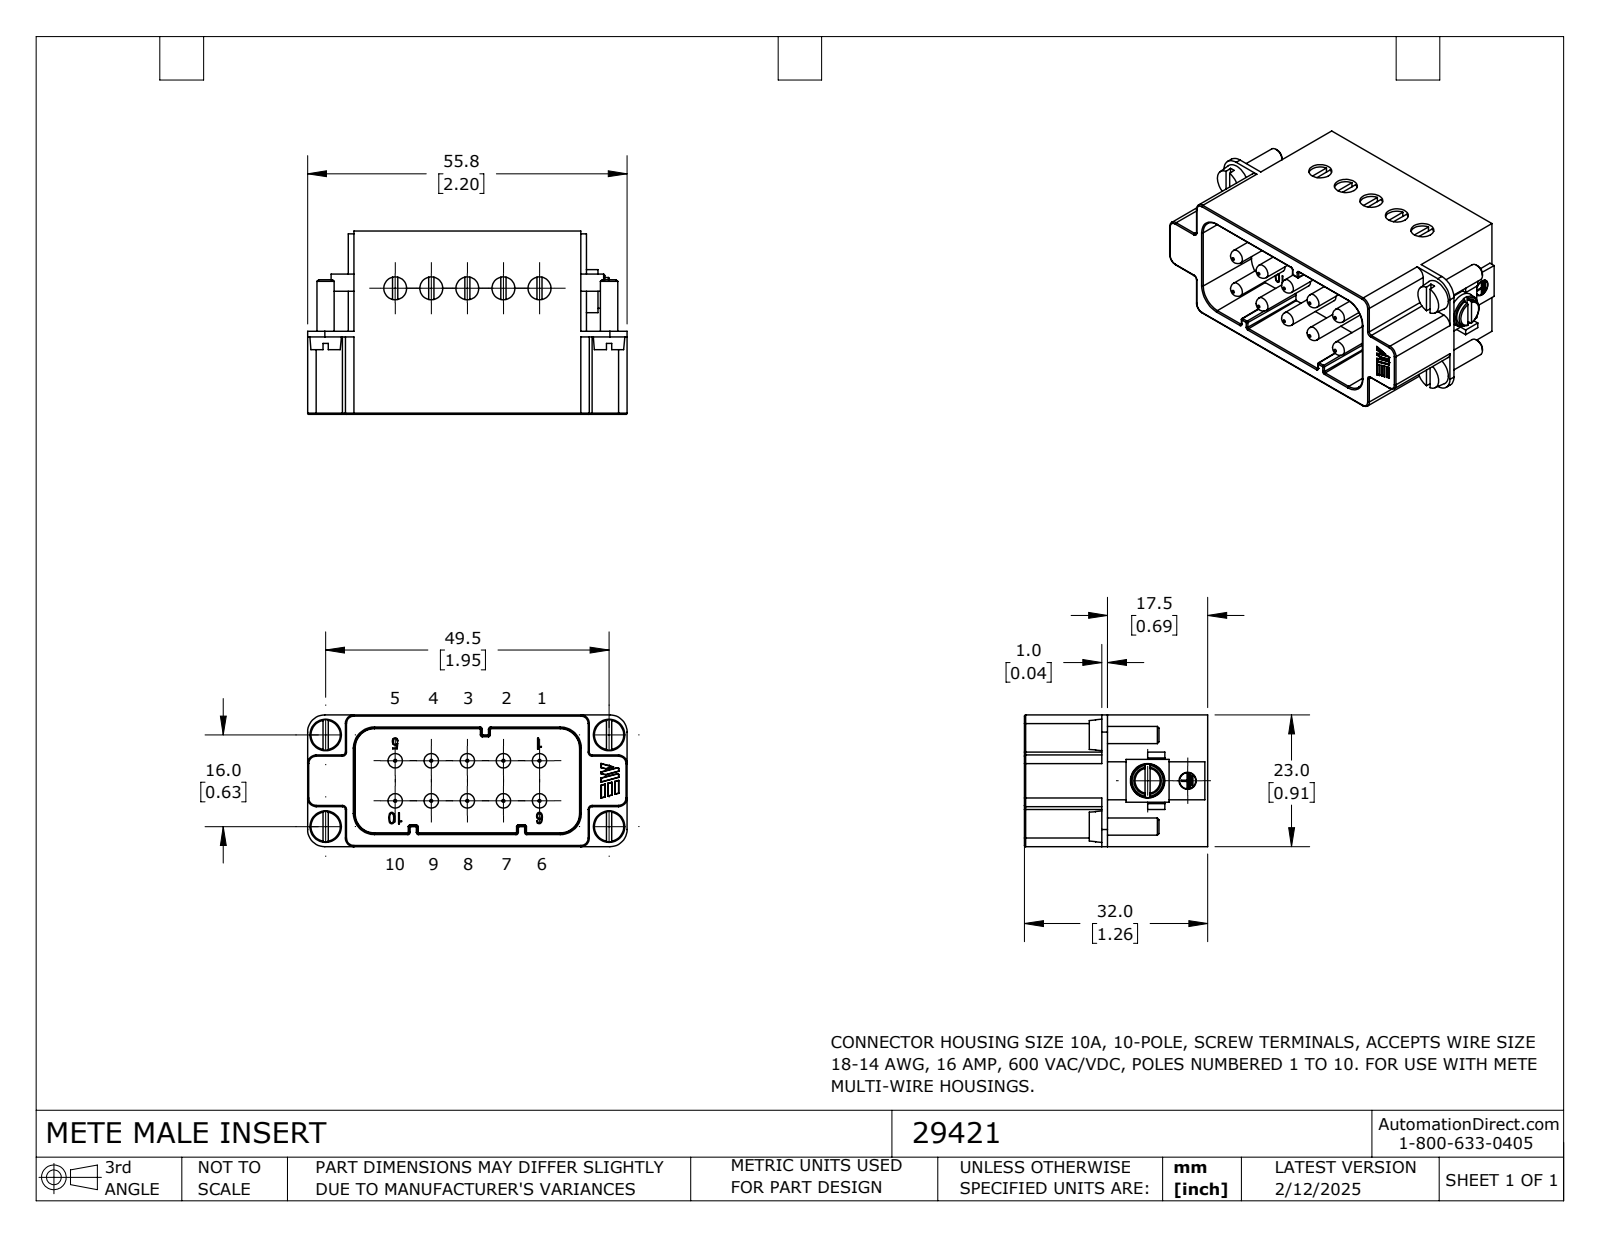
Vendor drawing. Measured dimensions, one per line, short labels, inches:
name: 29421
written by: SolidWorks 2024 (CONFIG_CONTROL_DESIGN)
unit: in
bodies: 1 solid, 522 faces (261 planar, 146 cylindrical, 115 other)
size: 2.197 × 1.26 × 0.906
volume: 1.404 in³; area: 18.64 in²
holes: 15× ⌀0.157, 1× ⌀0.118
bosses: 10× ⌀0.098, 4× ⌀0.118, 1× ⌀0.189, 1× ⌀0.11
rounds: 20× R0.008, 8× R0.059, 4× R0.02, 4× R0.118
face distances: 0.906, 0.787, 0.098, 0.059, 0.02, 0.571, 0.472, 0.689, 1.26, 0.039
hole spacings: 0.248, 0.496, 0.371, 0.567, 0.744, 0.276, 0.793, 0.992
